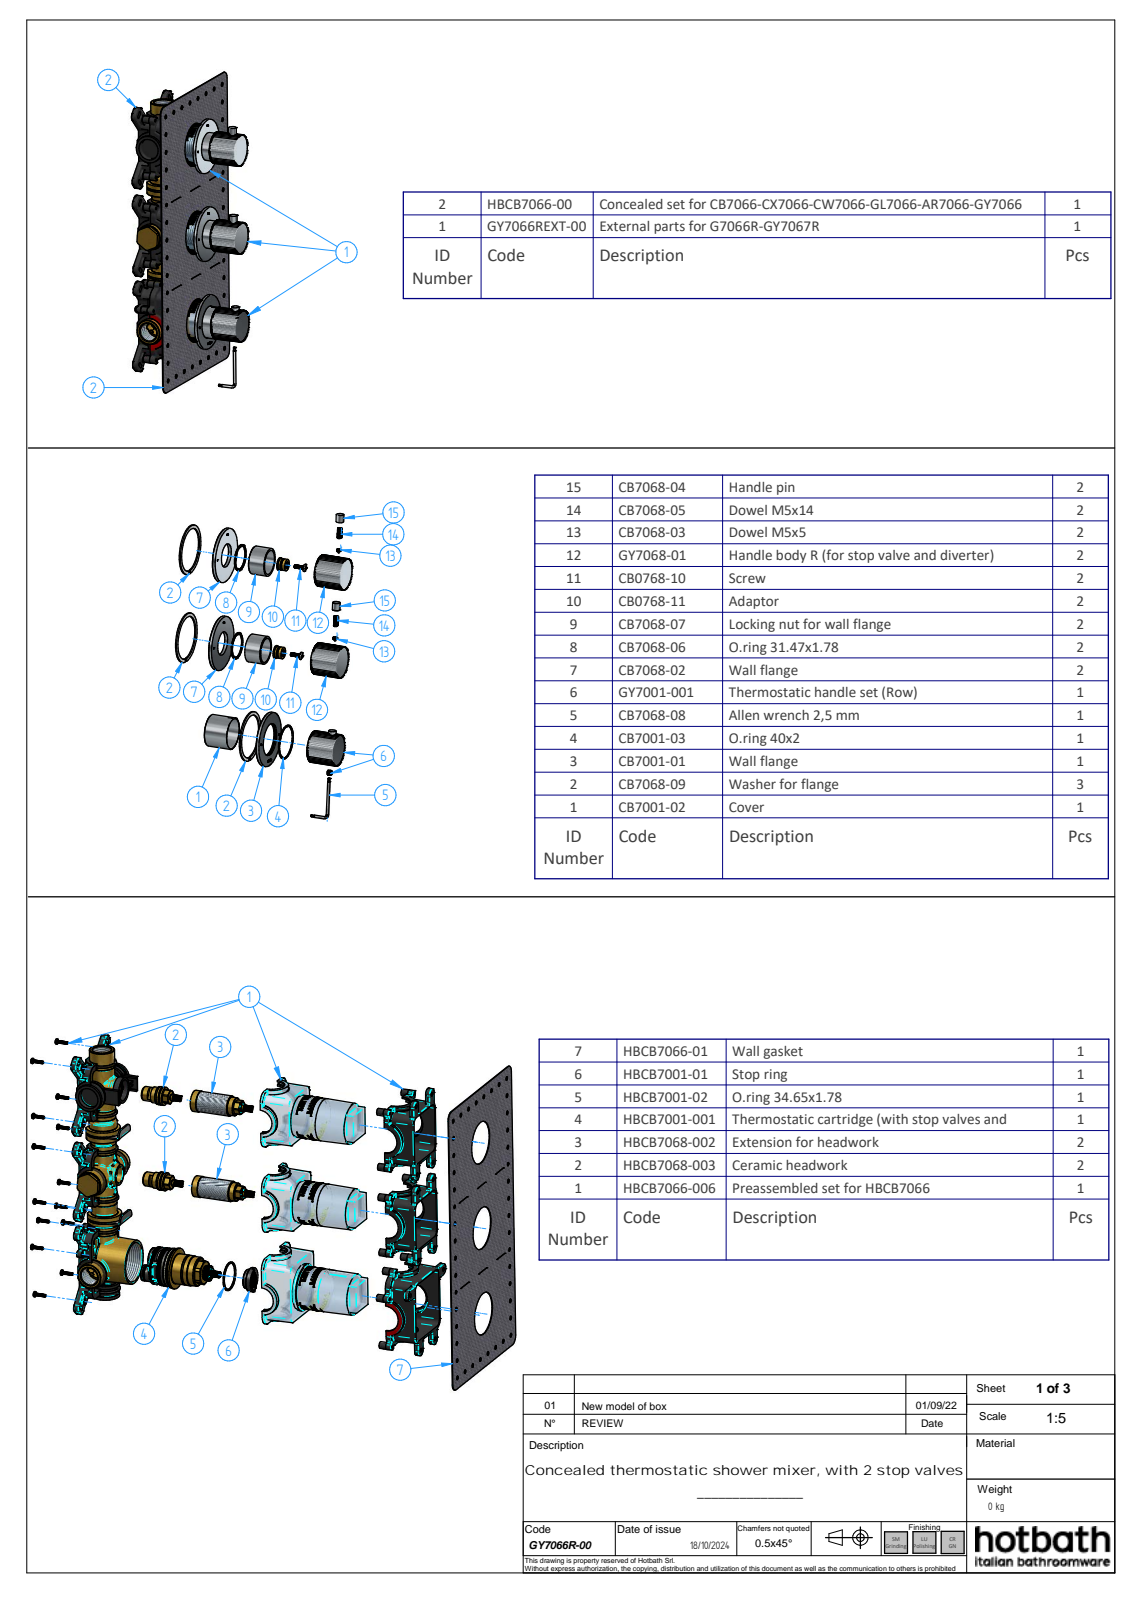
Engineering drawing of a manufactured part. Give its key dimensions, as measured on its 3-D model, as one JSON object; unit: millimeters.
{"part_name": "GY7066REXT-00; CB7001-02; CB7001-01; GY7001-001_oa_0 (+6 more)", "step_written_by": "Solid Edge (AUTOMOTIVE_DESIGN)", "units": "millimeters", "bodies": {"solids": 12, "faces": 2657, "planar": 607, "cylindrical": 868, "other": 1182}, "overall_size": [312, 72, 68.31], "volume_mm3": 102319, "surface_area_mm2": 87172, "round_holes": [[38, 3], [67, 3], [4, 2], [5.2, 2], [15.2, 2], [25.5, 2], [31, 2], [32, 2], [35, 2], [37, 2], [2.46, 1], [3.2, 1]], "round_bosses_or_shafts": [[72, 3], [57, 3], [10, 2], [42, 1], [13, 1], [7.5, 1], [4.5, 1]], "partial_cylinders_radius": [[0.1, 531], [4.5, 12], [9.5, 3], [0.2, 2], [0.56, 2], [0.73, 2], [1, 2], [2.1, 2]], "face_to_face_distances": [4, 52.1, 48.1, 3, 1, 51.1, 46.1, 50.1, 49.1, 2], "hole_center_spacings": [120, 12.5, 107.5, 1.95, 2, 14.9, 92.6, 105.1]}
